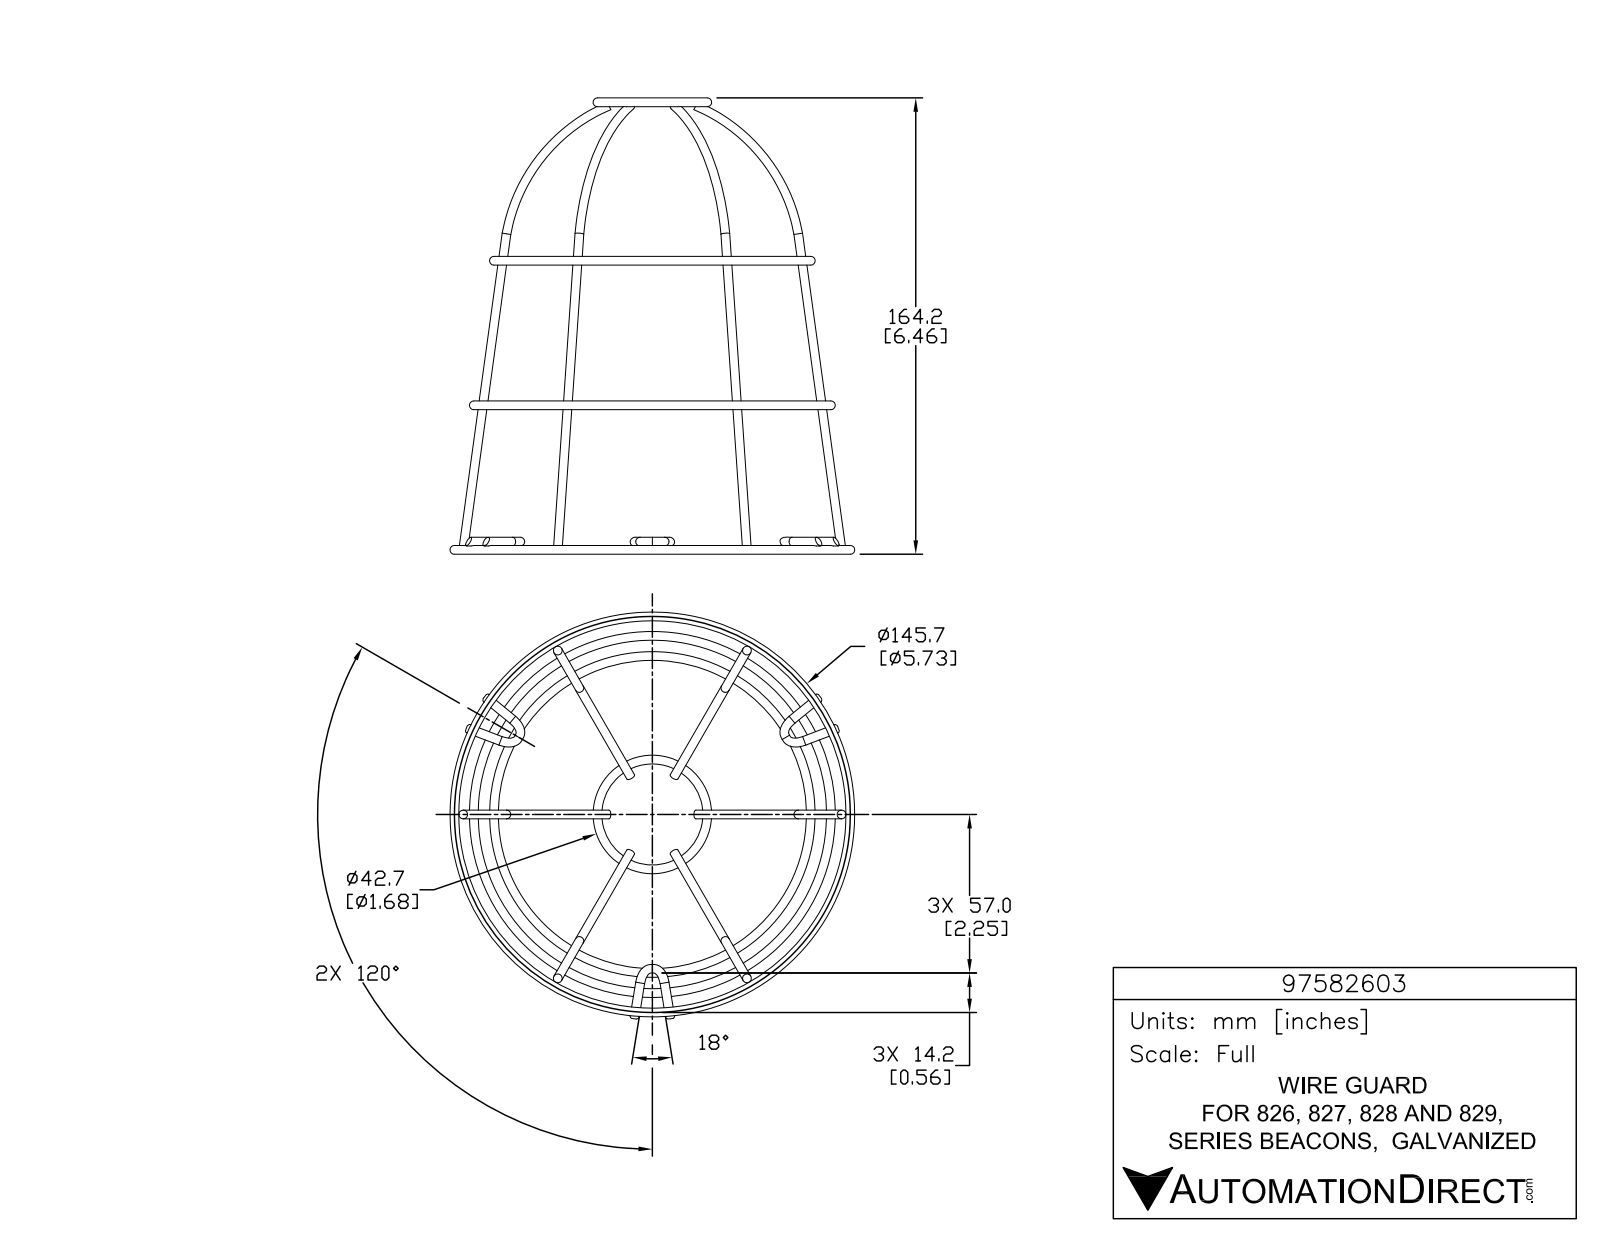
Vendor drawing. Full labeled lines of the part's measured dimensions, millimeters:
Part name (STEP PRODUCT): 97582603
STEP written by: SolidWorks 2017 (AUTOMOTIVE_DESIGN)
Units: millimetres
Bodies: 4 solids, 88 faces (12 planar, 0 cylindrical, 76 other)
Overall size (bounding box): 164.15 × 146.43 × 145.65
Volume: 19 698 mm³ · Surface area: 24 888 mm²
